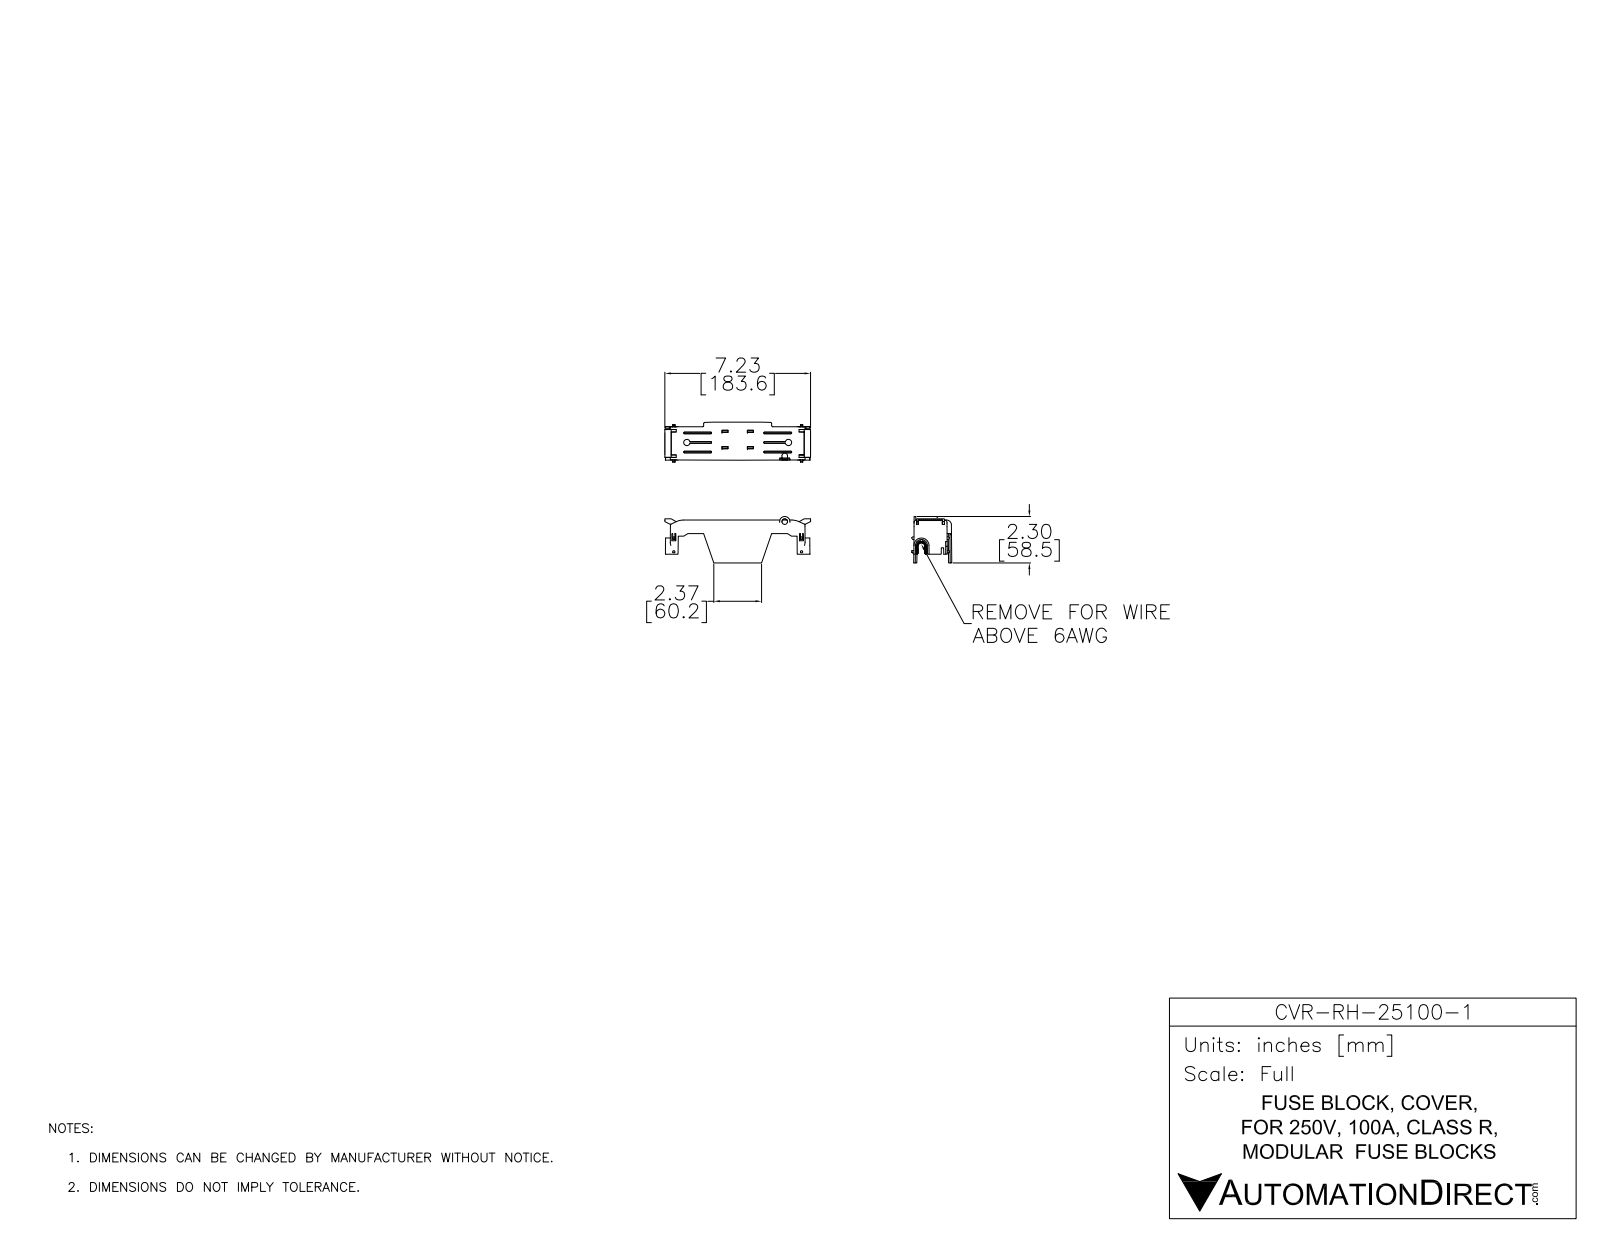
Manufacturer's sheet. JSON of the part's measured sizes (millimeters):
{"part_name": "CVR-RH-25100-1", "step_written_by": "SolidWorks 2017 (AUTOMOTIVE_DESIGN)", "units": "millimeters", "bodies": {"solids": 1, "faces": 1324, "planar": 879, "cylindrical": 102, "other": 343}, "overall_size": [183.6, 58.5, 50.4], "volume_mm3": 51650, "surface_area_mm2": 55220, "partial_cylinders_radius": [[1, 18], [3, 14], [0.8, 6], [1.5, 4], [0.3, 2], [0.5, 2], [2, 2], [3.5, 2]], "face_to_face_distances": [2, 5.5, 3.5, 7.5, 14.4, 3, 5, 57, 8.8, 12]}
